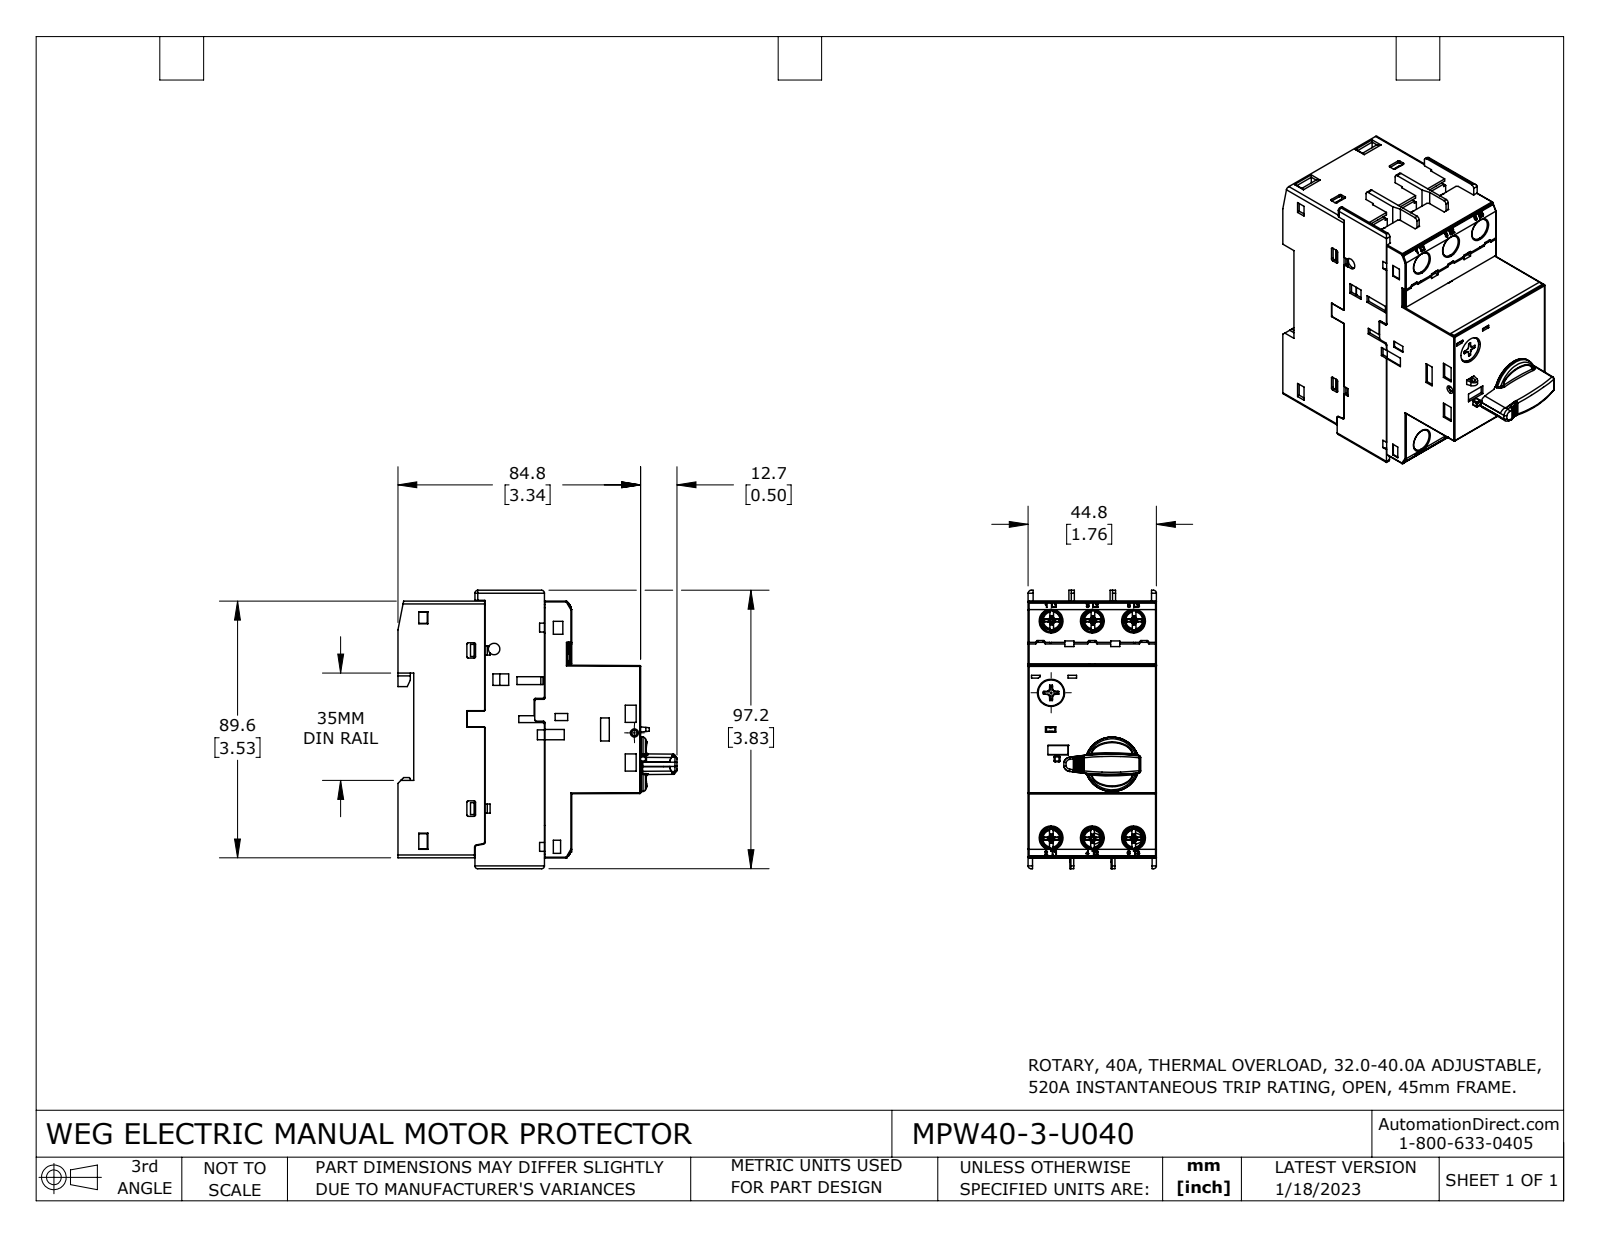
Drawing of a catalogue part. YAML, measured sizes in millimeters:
part_name: "MPW40-3-U040"
step_written_by: "SolidWorks 2021 (CONFIG_CONTROL_DESIGN)"
units: millimeters
bodies: {solids: 24, faces: 2323, planar: 1534, cylindrical: 345, other: 444}
overall_size: [97.5, 97.2, 44.8]
volume: 263700
surface_area: 58500
round_holes:
  - {diameter: 3.2, count: 6}
  - {diameter: 1.9, count: 1}
  - {diameter: 4, count: 1}
  - {diameter: 9.5, count: 1}
  - {diameter: 13.1, count: 1}
round_bosses_or_shafts:
  - {diameter: 5, count: 6}
  - {diameter: 4, count: 6}
  - {diameter: 3.3, count: 6}
  - {diameter: 3, count: 6}
  - {diameter: 19, count: 1}
  - {diameter: 10.9, count: 1}
  - {diameter: 9, count: 1}
partial_cylinders:
  - {radius: 0.5, count: 71}
  - {radius: 0.3, count: 41}
  - {radius: 1, count: 17}
  - {radius: 0.2, count: 6}
  - {radius: 15.2, count: 6}
  - {radius: 17, count: 6}
  - {radius: 0.7, count: 4}
  - {radius: 0.6, count: 3}
face_to_face_distances: [44.8, 45.7, 45.8, 79.3, 33.6, 33.5, 89.6, 9.5, 55.2, 9.4]
hole_center_spacings: [14.4, 76.2, 28.8, 77.5, 77.6, 25.3, 26.8, 27]
